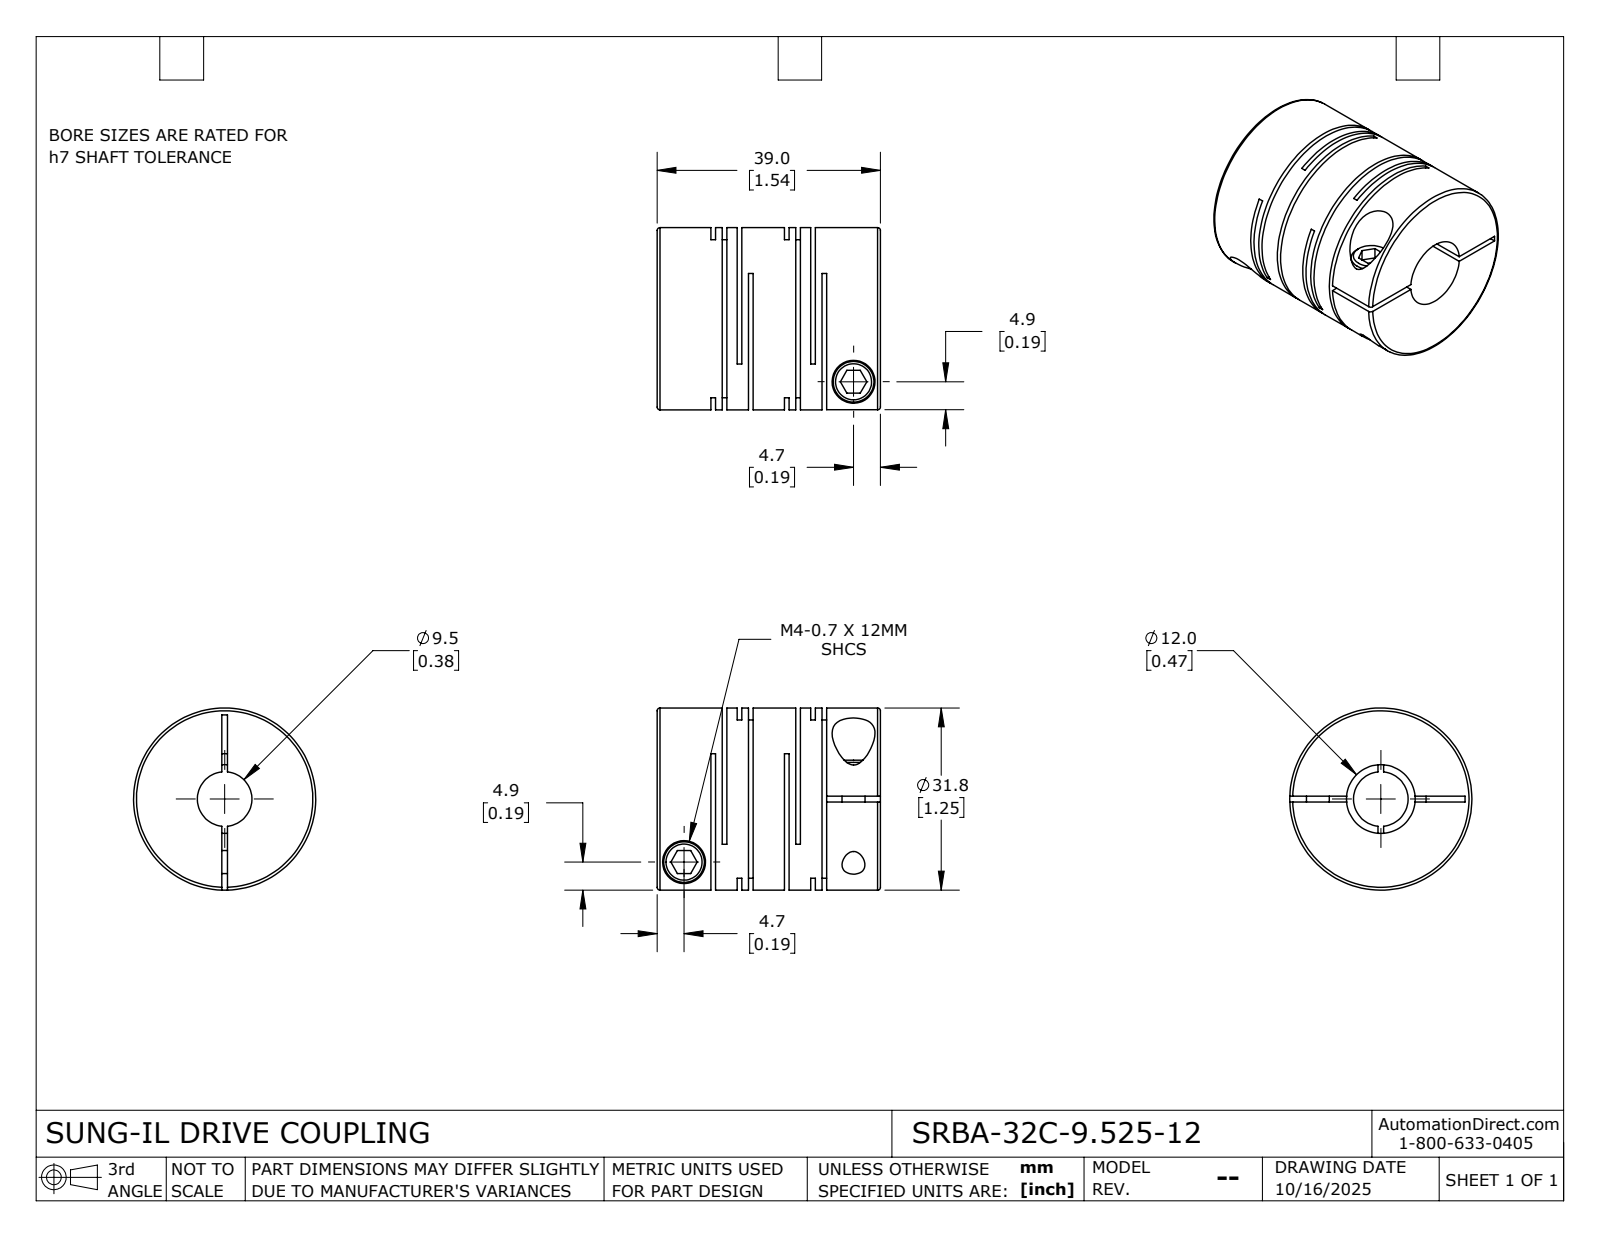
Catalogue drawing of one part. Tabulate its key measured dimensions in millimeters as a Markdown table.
| quantity | value |
| --- | --- |
| part name | SRBA-32C-9.525-12 |
| STEP written by | SolidWorks 2024 (CONFIG_CONTROL_DESIGN) |
| units | millimeters |
| bodies | 1 solid, 115 faces (60 planar, 42 cylindrical, 13 other) |
| overall size | 39 × 31.8 × 31.8 |
| volume | 22 710 mm³ |
| surface area | 15 773 mm² |
| round holes (diameter × count) | 4 × 2, 7.5 × 2, 9.53 × 1, 12 × 1 |
| round bosses / shafts (diameter × count) | 7.1 × 2, 31.8 × 1 |
| main face-to-face distances | 0.8, 12.84, 1.98, 4.58, 12.04, 1.18, 10.86, 3.78, 8.26, 2.6 |
